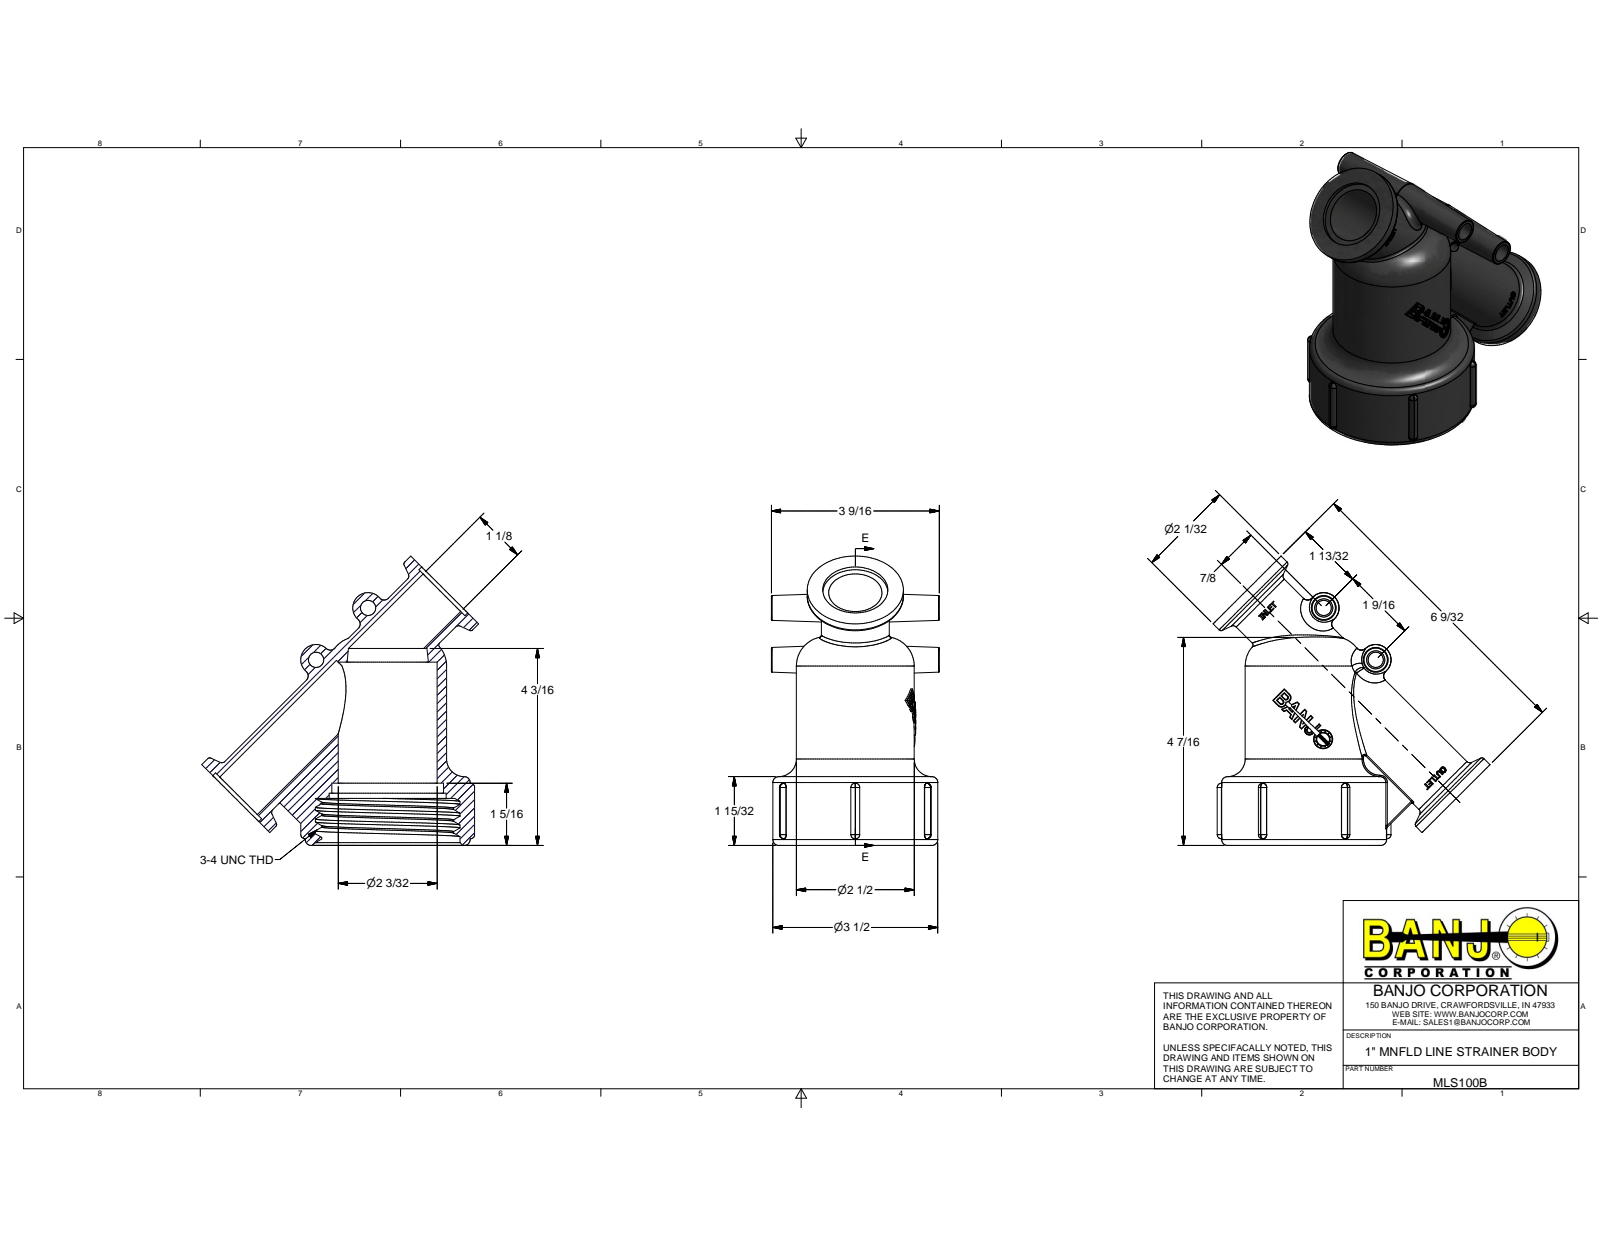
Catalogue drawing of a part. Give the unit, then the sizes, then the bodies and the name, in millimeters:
Units: millimetres
Overall size (bounding box): 156.21 × 149.25 × 90.49
Round holes (diameter × count): ⌀28.7 ×2, ⌀35.05 ×2, ⌀6.92 ×1, ⌀9.77 ×1, ⌀53.34 ×1, ⌀60.22 ×1, ⌀62.99 ×1, ⌀71.1 ×1, ⌀77.98 ×1
Round bosses / shafts (diameter × count): ⌀51.82 ×2, ⌀88.9 ×1, ⌀63.5 ×1, ⌀36.58 ×1, ⌀10.29 ×1
Partial cylindrical surfaces — rounded edges, fillets, slot ends (radius × count): R2.29 ×35, R0.76 ×8, R0.99 ×2, R1.25 ×2, R2.41 ×2, R2.67 ×2, R1.25 ×1, R1.51 ×1
Main face-to-face distances: 159.23, 73.53, 2.13, 157.1, 8.25, 65.28, 80.9, 72.65, 7.37, 154.97
Volume: 240 705 mm³ · Surface area: 94 187 mm²
Bodies: 1 solid, 676 faces (391 planar, 153 cylindrical, 132 other)
Part name (STEP PRODUCT): MLS100B
STEP written by: Autodesk Inventor 2015 (AUTOMOTIVE_DESIGN)
